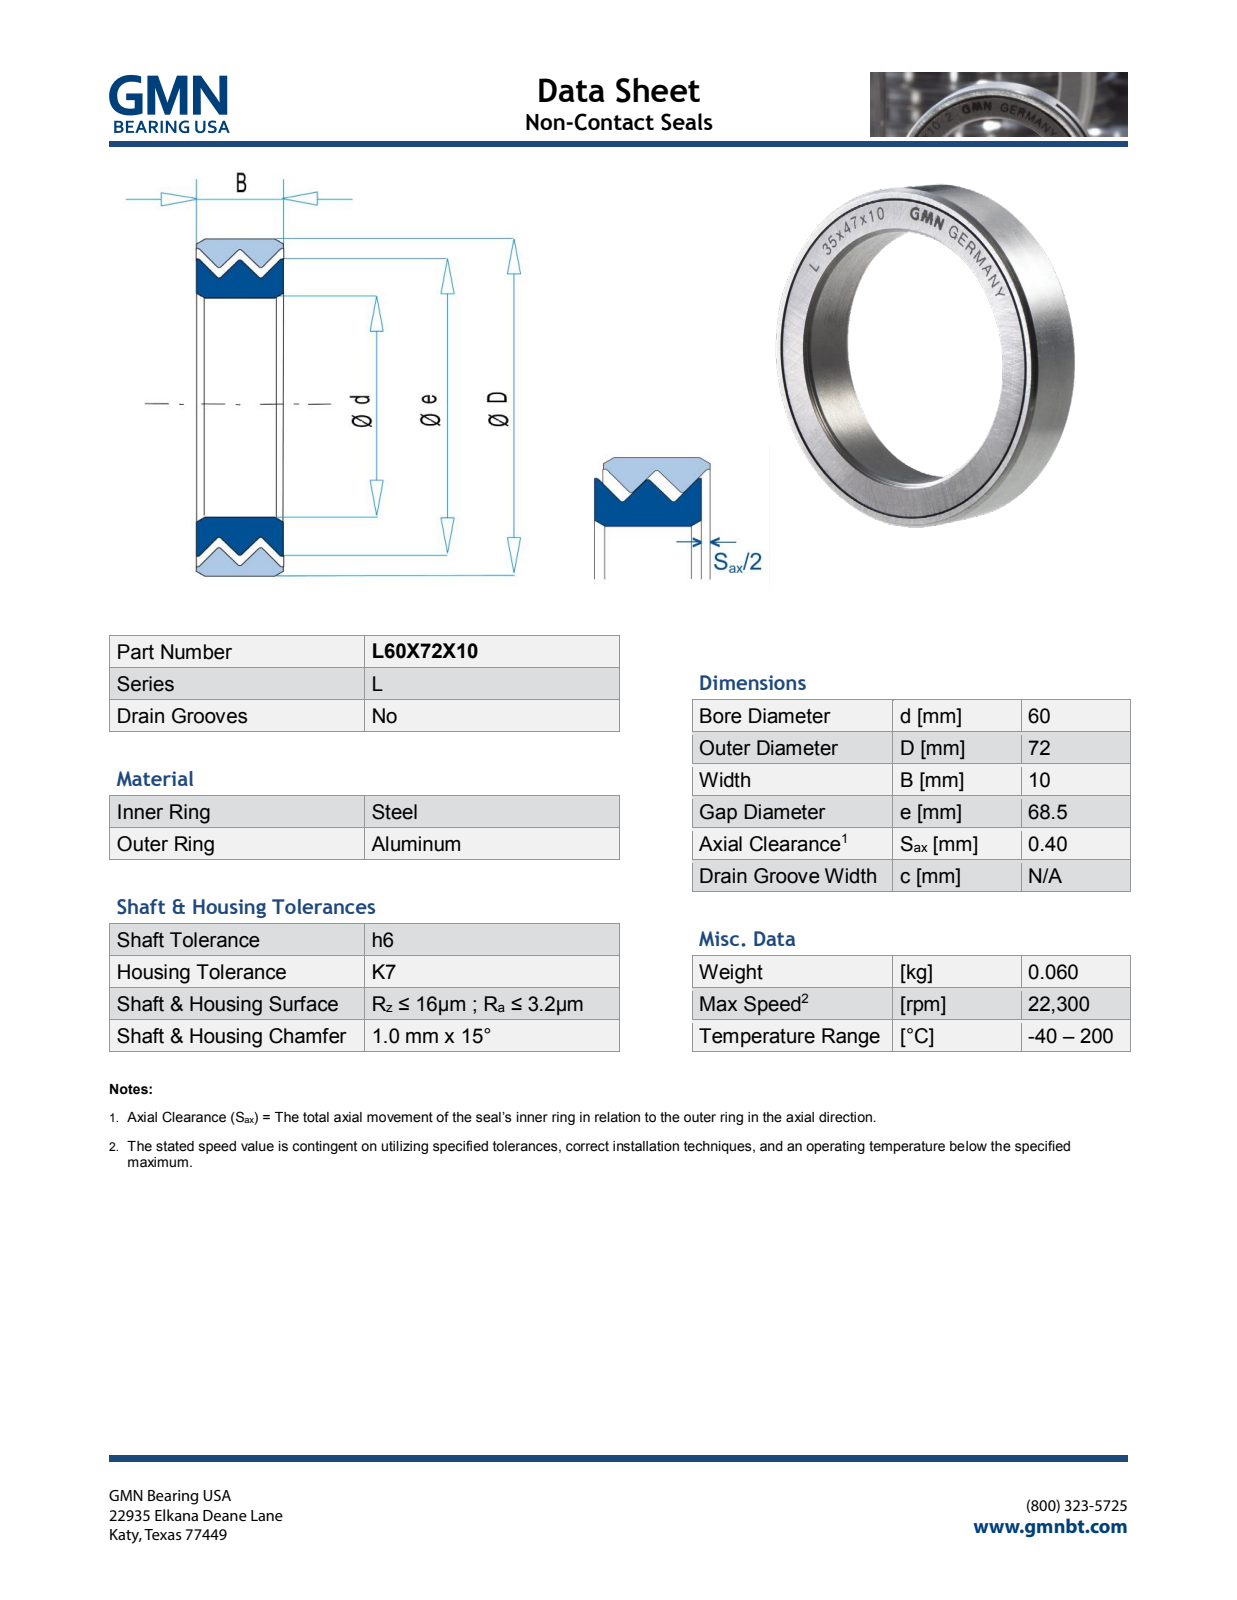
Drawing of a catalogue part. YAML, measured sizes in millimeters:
part_name: "L60X72X10_PRT"
step_written_by: "PRO/ENGINEER BY PARAMETRIC TECHNOLOGY CORPORATION, 2013150 (AUTOMOTIVE_DESIGN)"
units: millimeters
bodies: {solids: 2, faces: 566, planar: 510, cylindrical: 12, other: 44}
overall_size: [72, 72, 10.07]
volume: 11808
surface_area: 11821
round_holes:
  - {diameter: 60, count: 1}
  - {diameter: 68.78, count: 1}
round_bosses_or_shafts:
  - {diameter: 72, count: 1}
  - {diameter: 68.5, count: 1}
face_to_face_distances: [10, 10.07, 1.67, 1.47, 1.19, 1.46, 1.26, 1.68, 1.4, 1.08]
